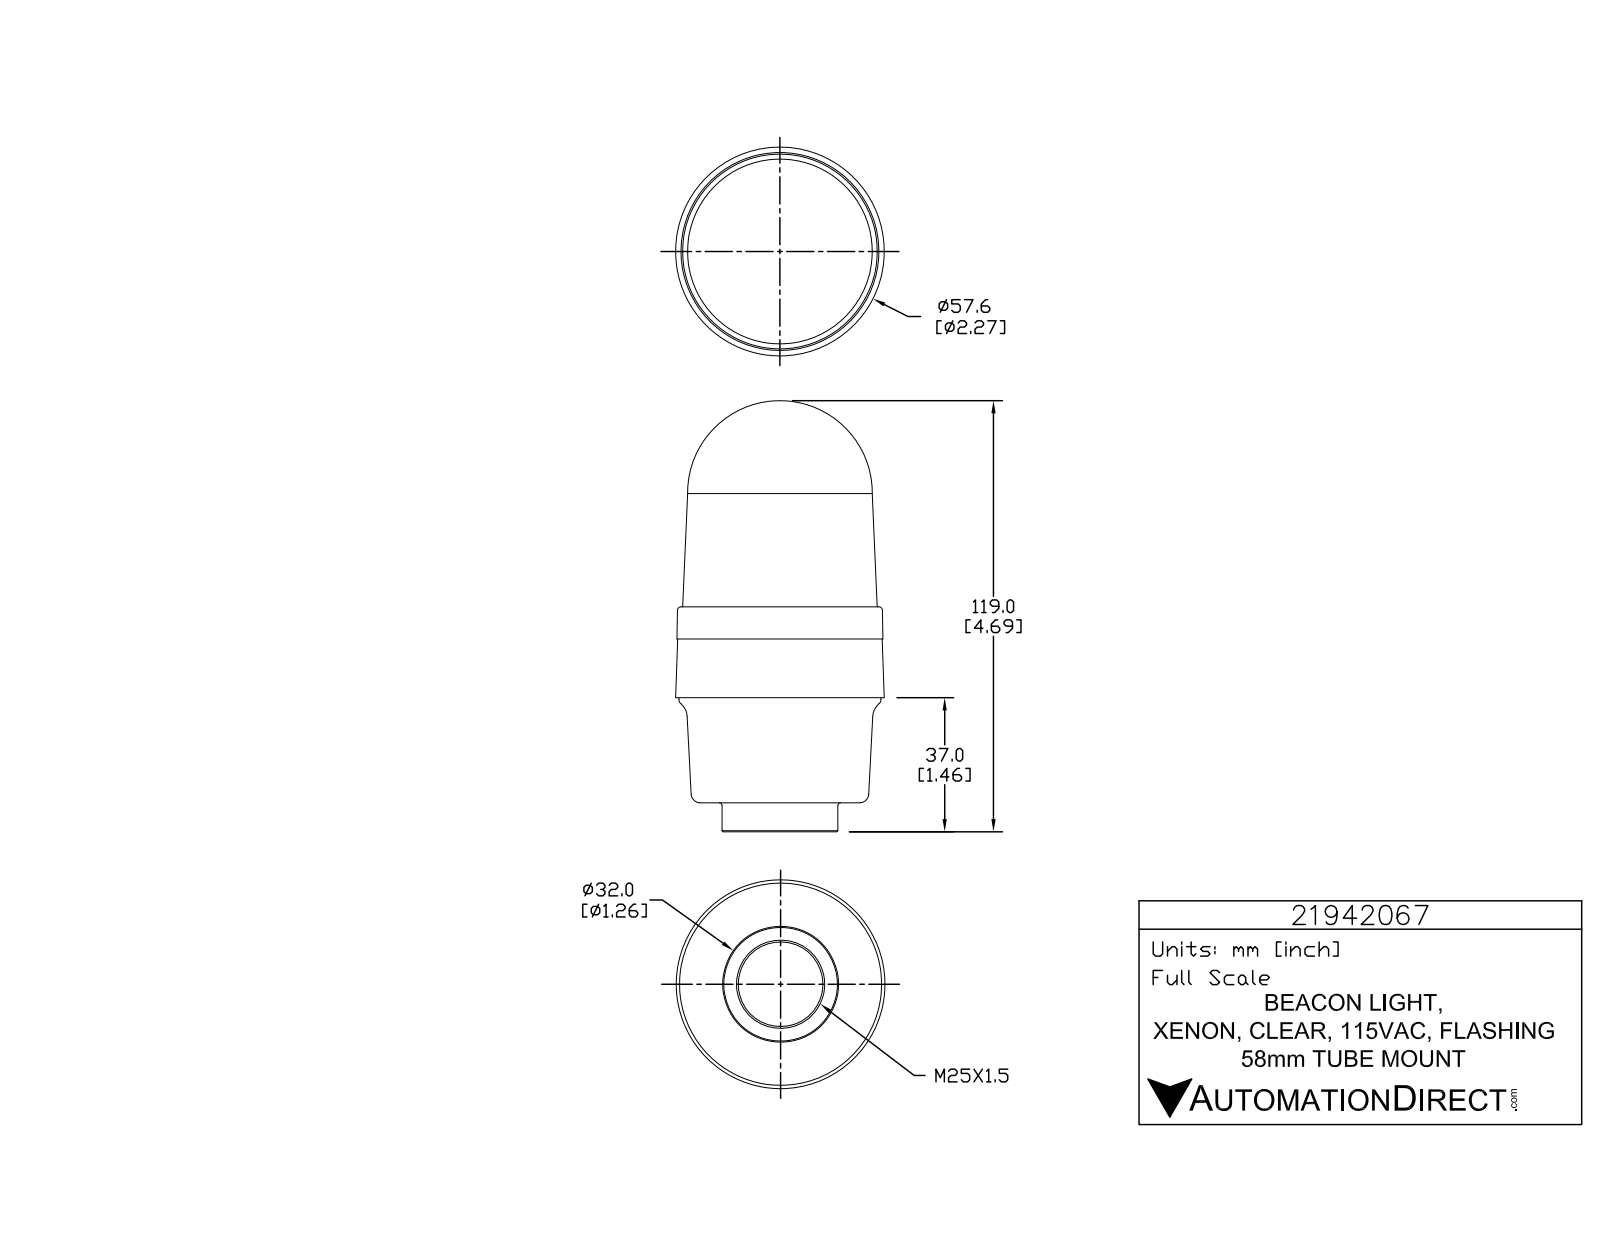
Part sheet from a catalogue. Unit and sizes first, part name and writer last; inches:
Units: inches
Overall size (bounding box): 4.685 × 2.269 × 2.269
Round holes (diameter × count): ⌀0.039 ×3, ⌀0.92 ×1
Round bosses / shafts (diameter × count): ⌀0.226 ×3, ⌀0.056 ×3, ⌀2.197 ×1, ⌀1.26 ×1
Partial cylindrical surfaces — rounded edges, fillets, slot ends (radius × count): R0.008 ×6, R0.008 ×6, R0.008 ×6, R0.131 ×6, R0.004 ×3, R0.005 ×3, R0.008 ×3, R0.008 ×3
Main face-to-face distances: 0.315, 1.142, 1.457, 0.988, 2.13, 2.445, 0.35, 0.638, 1.78, 2.094
Volume: 13.89 in³ · Surface area: 34.06 in²
Bodies: 1 solid, 791 faces (525 planar, 168 cylindrical, 98 other)
Part name (STEP PRODUCT): 21942067
STEP written by: SolidWorks 2015 (AUTOMOTIVE_DESIGN)
